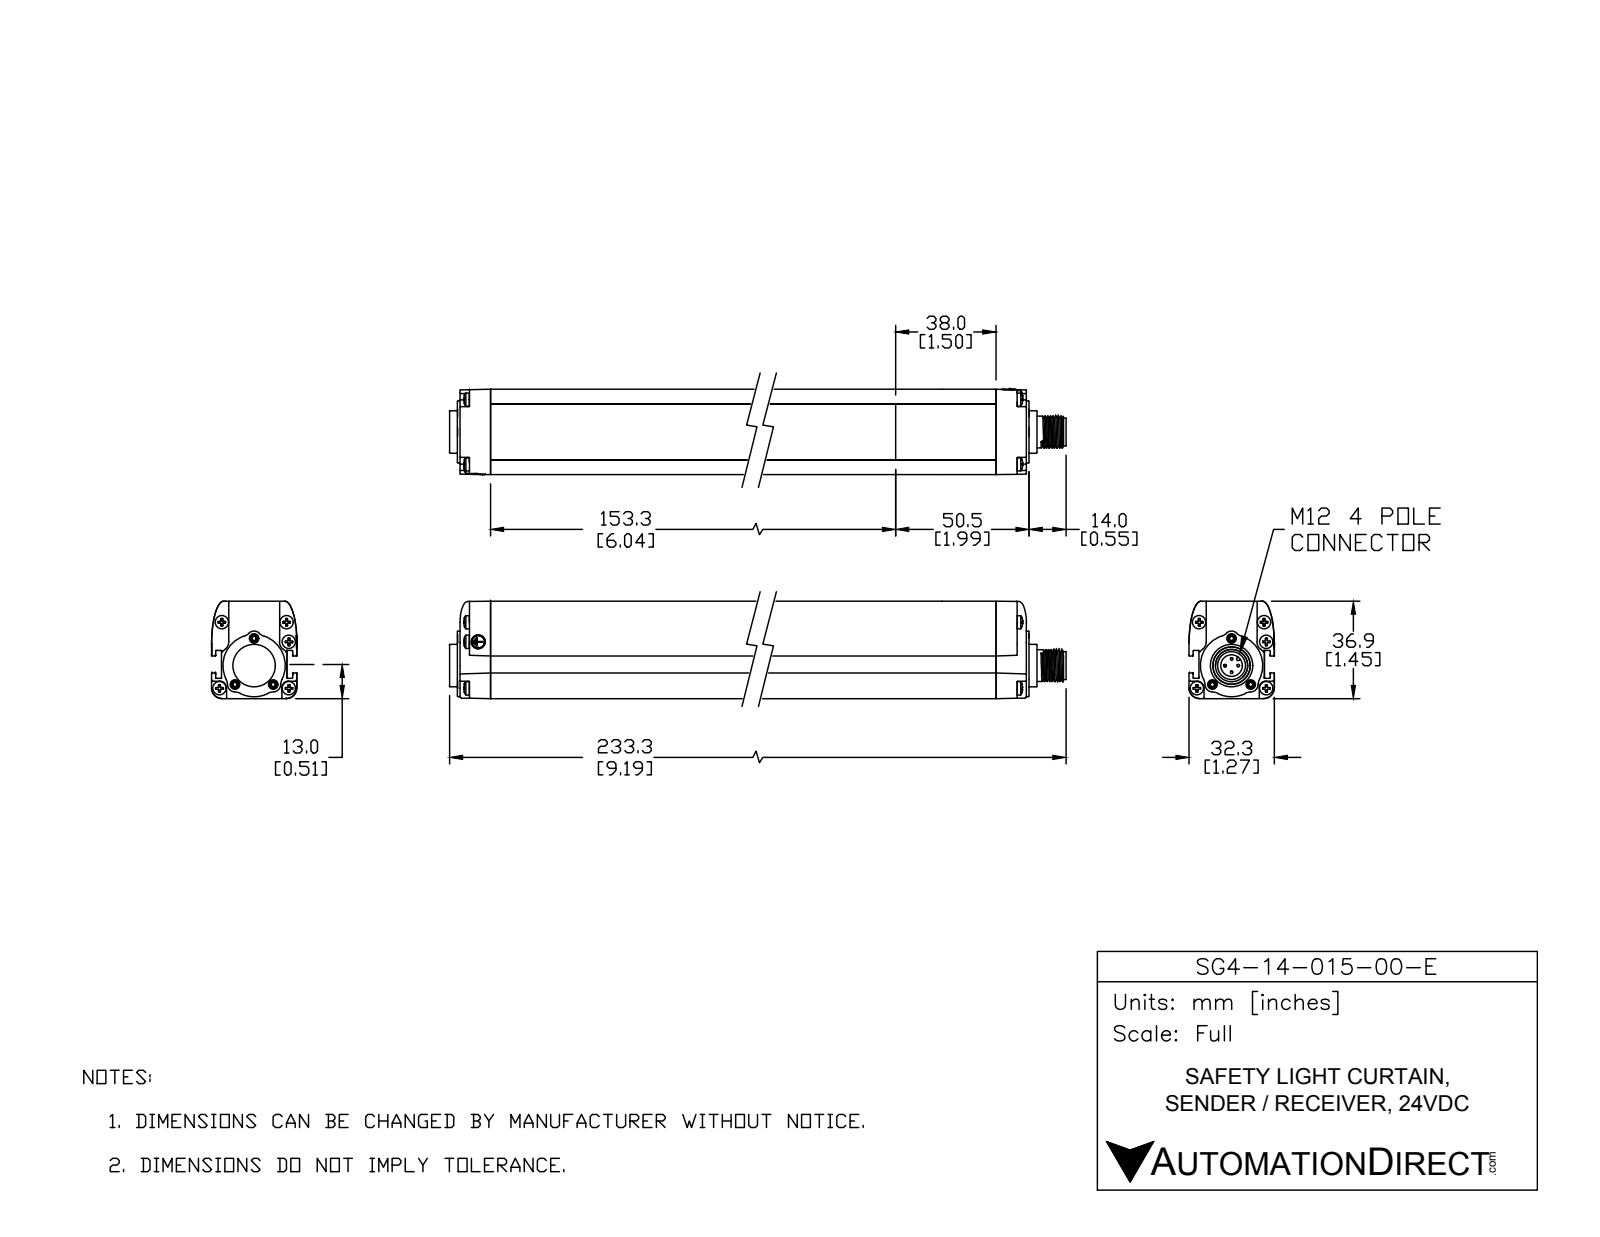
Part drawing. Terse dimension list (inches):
name: SG4-14-015-00-E
written by: SolidWorks 2017 (AUTOMOTIVE_DESIGN)
unit: in
bodies: 29 solids, 1669 faces (410 planar, 588 cylindrical, 671 other)
size: 9.185 × 2.481 × 2.069
volume: 14.47 in³; area: 112.7 in²
holes: 10× ⌀0.106, 6× ⌀0.059, 6× ⌀0.142, 6× ⌀0.209, 4× ⌀0.081, 4× ⌀0.165, 4× ⌀0.26, 1× ⌀0.323, 1× ⌀0.376, 1× ⌀0.433, 1× ⌀0.563
bosses: 14× ⌀0.197, 4× ⌀0.394, 4× ⌀0.039, 2× ⌀0.63, 2× ⌀0.185, 1× ⌀0.55, 1× ⌀0.472, 1× ⌀0.413
rounds: 168× R0.008, 152× R0.004, 20× R0.106, 18× R0.006, 13× R0.197, 8× R0.118, 6× R0.11, 4× R0.14
face distances: 0.079, 0.15, 0.118, 1.272, 1.429, 1.122, 1.35, 0.157, 0.268, 7.531
hole spacings: 0.541, 1.403, 0.903, 1.205, 0.24, 0.402, 0.569, 0.742
